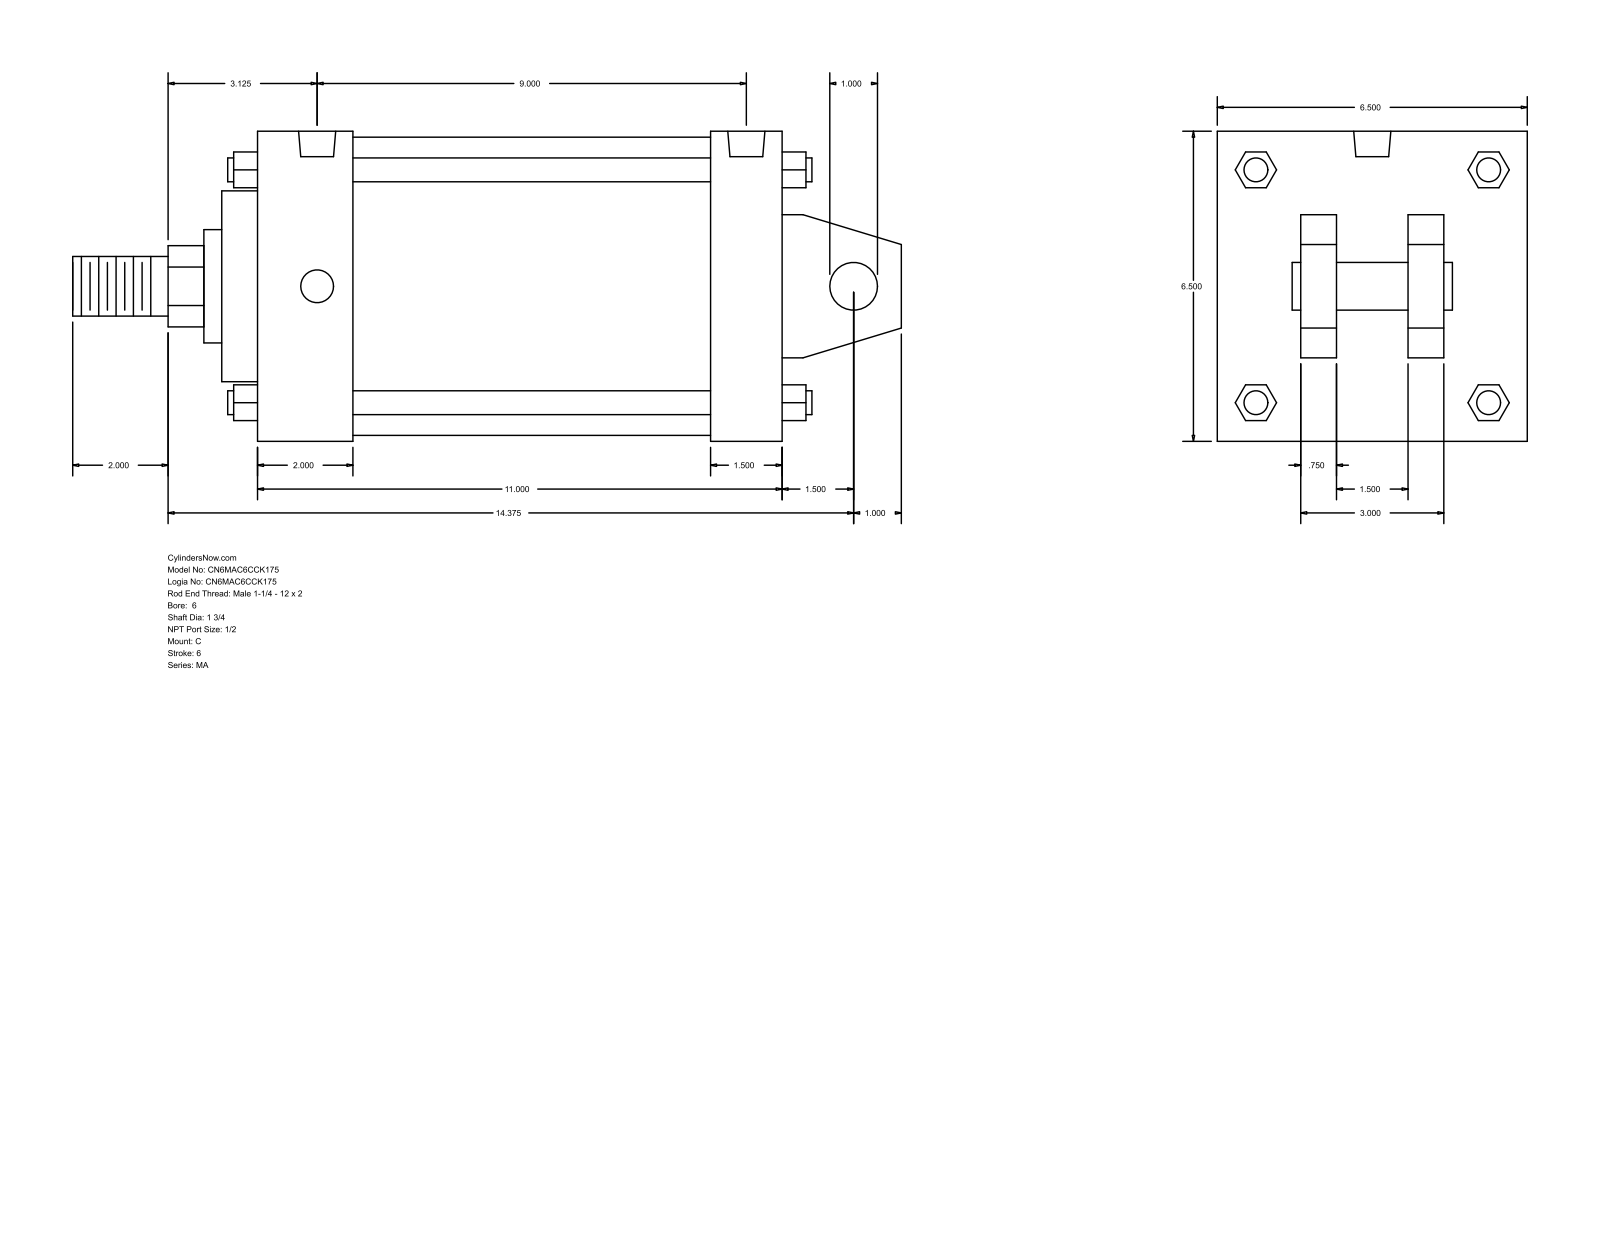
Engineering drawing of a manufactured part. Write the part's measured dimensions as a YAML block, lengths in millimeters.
part_name: "MA_C__0600_1.75"
step_written_by: "GSSL Pune (CONFIG_CONTROL_DESIGN)"
units: millimeters
bodies: {solids: 0, faces: 141, planar: 109, cylindrical: 32, other: 0}
overall_size: [441.32, 165.1, 165.1]
round_holes:
  - {diameter: 17.46, count: 4}
  - {diameter: 19.77, count: 2}
round_bosses_or_shafts:
  - {diameter: 12.7, count: 4}
  - {diameter: 158.75, count: 1}
  - {diameter: 101.6, count: 1}
  - {diameter: 60.33, count: 1}
  - {diameter: 44.45, count: 1}
  - {diameter: 31.75, count: 1}
  - {diameter: 25.4, count: 1}
partial_cylinders:
  - {radius: 21.63, count: 1}
face_to_face_distances: [165.1, 279.4, 19.05, 63.5, 101.6, 50.8, 120.65, 44.45, 241.31, 57.15]
hole_center_spacings: [228.6]
